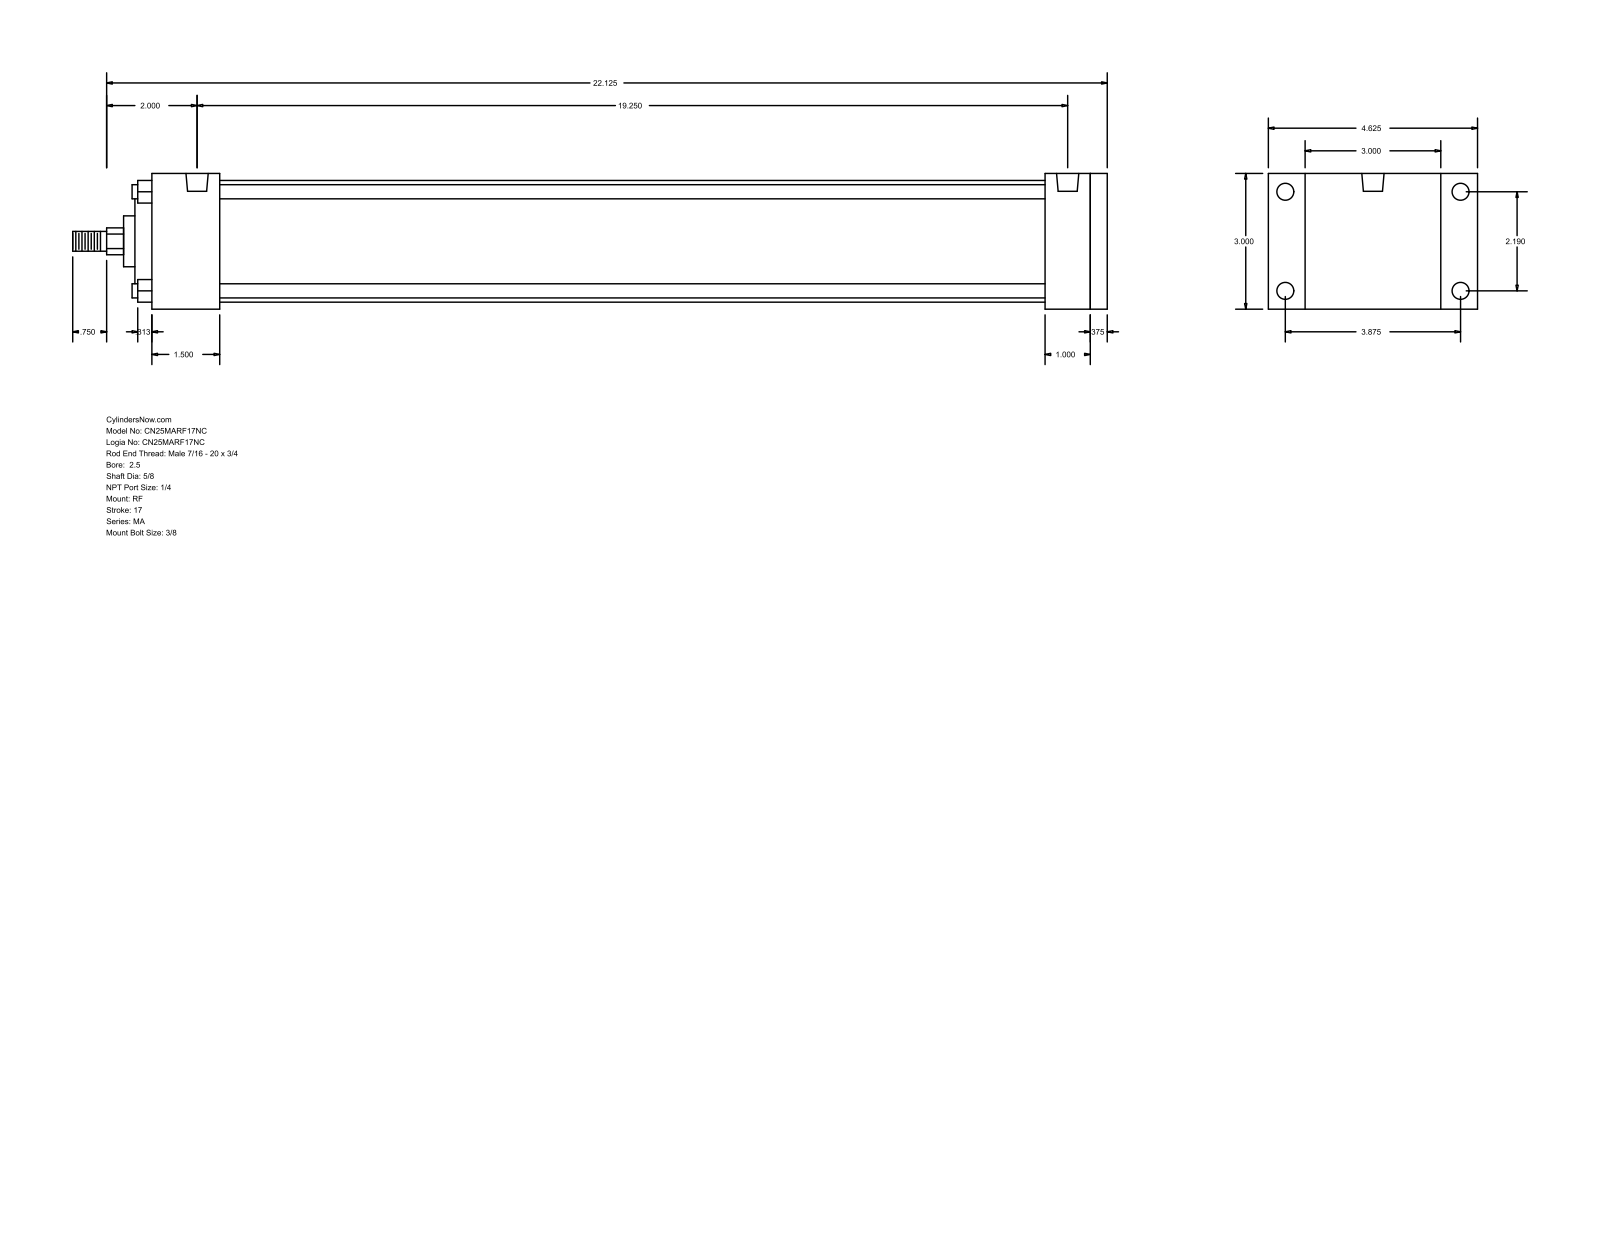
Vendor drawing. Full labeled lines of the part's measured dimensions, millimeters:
Part name (STEP PRODUCT): MA_RF__0250_0.625
STEP written by: GSSL Pune (CONFIG_CONTROL_DESIGN)
Units: millimetres
Bodies: 0 solids, 94 faces (65 planar, 29 cylindrical, 0 other)
Overall size (bounding box): 581.02 × 117.47 × 76.2
Round holes (diameter × count): ⌀7.94 ×4, ⌀9.53 ×4, ⌀12.49 ×2
Round bosses / shafts (diameter × count): ⌀7.94 ×4, ⌀68.33 ×1, ⌀50.8 ×1, ⌀28.57 ×1, ⌀15.88 ×1, ⌀11.11 ×1
Partial cylindrical surfaces — rounded edges, fillets, slot ends (radius × count): R7.54 ×1
Main face-to-face distances: 76.2, 536.58, 9.53, 527.05, 25.4, 34.93, 38.1, 501.65, 463.55, 488.95
Hole centre spacings: 55.62, 98.42, 113.05, 488.95
